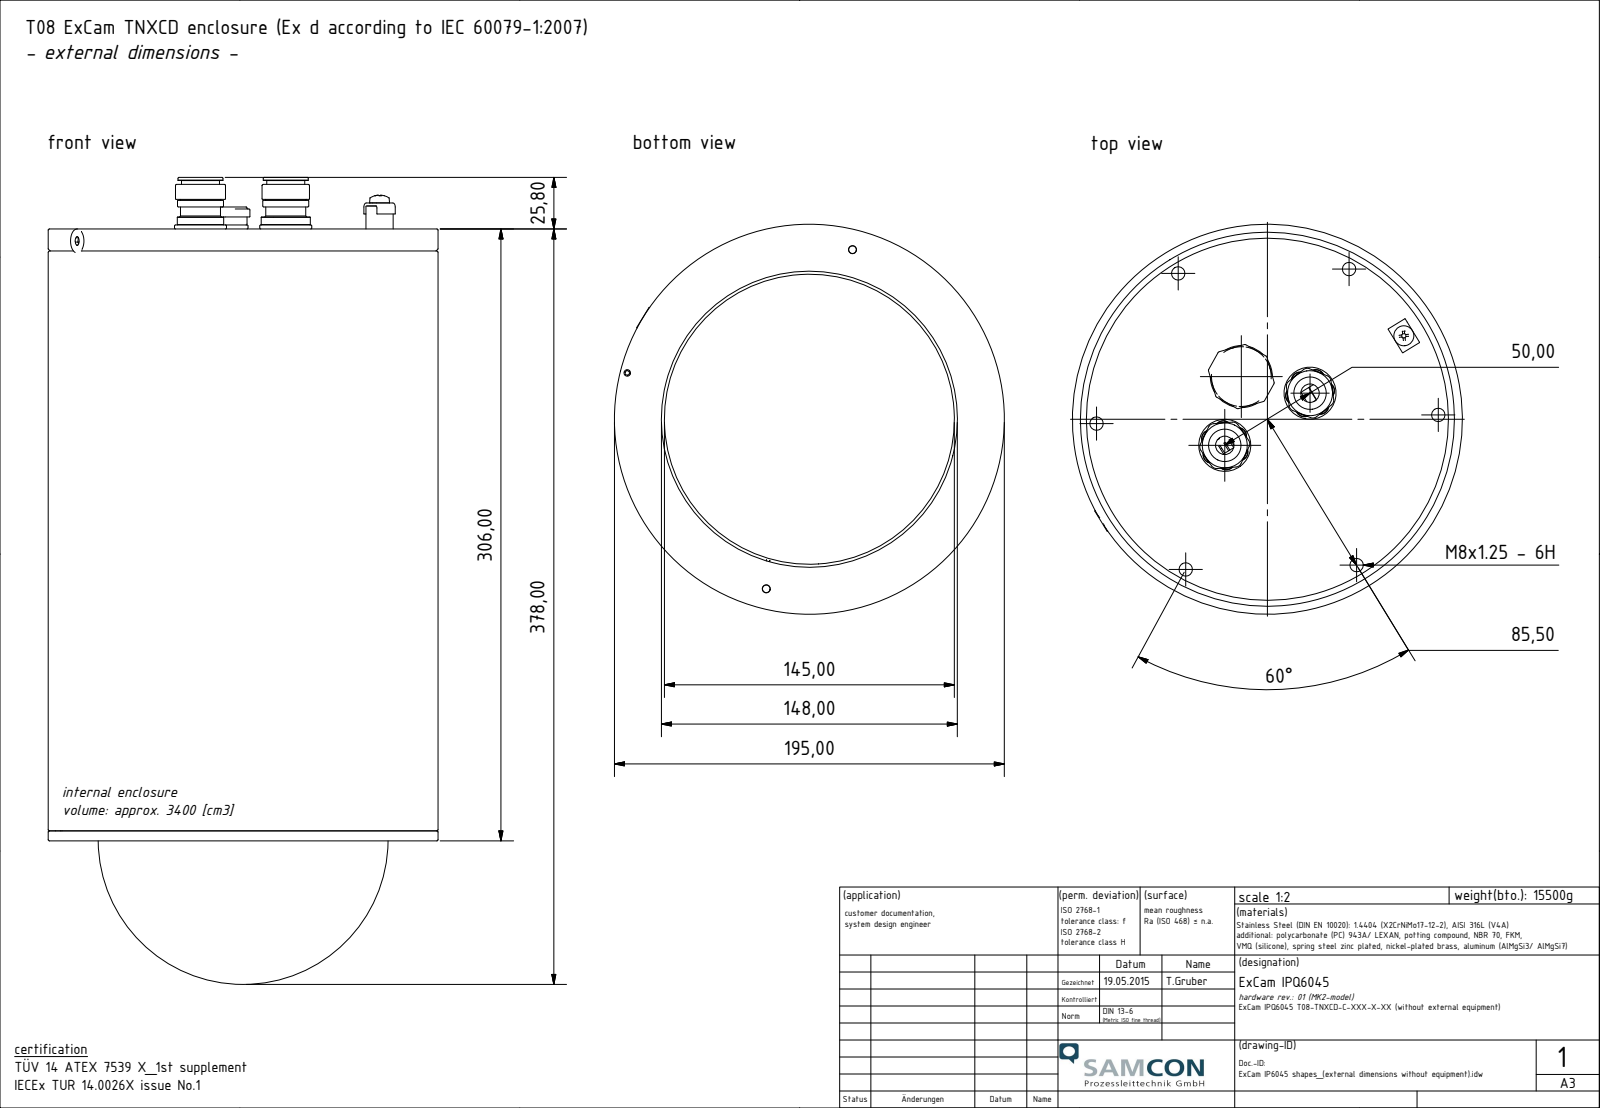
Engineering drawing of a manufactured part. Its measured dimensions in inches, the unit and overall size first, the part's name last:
Units: inches
Overall size (bounding box): 17.393 × 14.884 × 9.963
Round holes (diameter × count): ⌀0.262 ×6, ⌀0.194 ×5, ⌀0.157 ×2, ⌀0.163 ×2, ⌀0.228 ×2, ⌀0.723 ×2, ⌀0.128 ×1, ⌀0.177 ×1, ⌀0.331 ×1, ⌀0.457 ×1, ⌀0.63 ×1, ⌀0.635 ×1
Round bosses / shafts (diameter × count): ⌀0.118 ×8, ⌀0.197 ×2, ⌀0.181 ×2, ⌀7.677 ×1, ⌀7.402 ×1, ⌀7.39 ×1, ⌀7.244 ×1, ⌀7.22 ×1
Partial cylindrical surfaces — rounded edges, fillets, slot ends (radius × count): R0.008 ×64, R0.039 ×44, R0.004 ×28, R0.02 ×16, R0.012 ×12, R0.033 ×8, R0.079 ×4, R0.098 ×4
Main face-to-face distances: 0.827, 11.22, 12.047, 0.354, 11.693, 10.866, 10.551, 10.197, 0.669, 1.496
Hole centre spacings: 3.366, 3.507, 5.171, 6.46, 0.984, 3.366, 3.908, 4.454
Volume: 113.9 in³ · Surface area: 1 038 in²
Bodies: 23 solids, 1334 faces (251 planar, 320 cylindrical, 763 other)
Part name (STEP PRODUCT): T08-TNXCD_(EX D ENCLOSURE, CABLE ENTRY); XCD1953290W Ex d Leergehäuse (Typ LL); XCD-35-2 Sheet 1 (Rumpf); XCD-195 Compund (+8 more)
STEP written by: Autodesk Inventor 2022 (AUTOMOTIVE_DESIGN)
